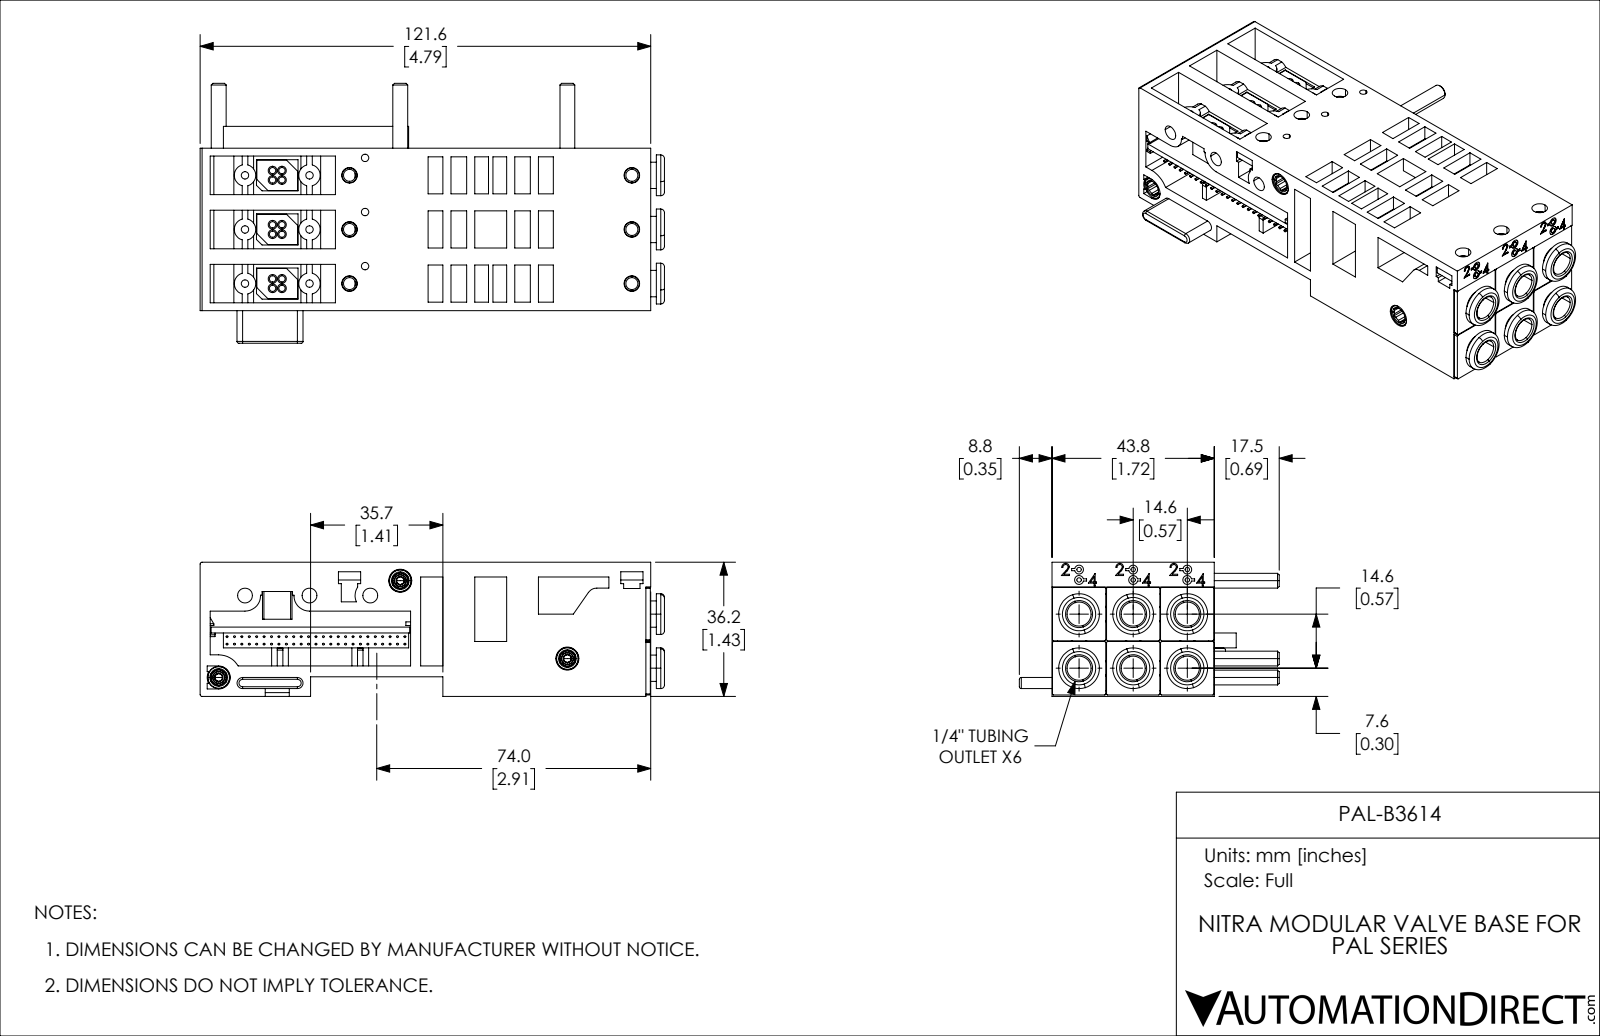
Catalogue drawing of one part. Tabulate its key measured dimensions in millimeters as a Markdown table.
| quantity | value |
| --- | --- |
| part name | PAL-B3614 |
| STEP written by | SolidWorks 2019 (CONFIG_CONTROL_DESIGN) |
| units | millimeters |
| bodies | 7 solids, 1501 faces (811 planar, 520 cylindrical, 170 other) |
| overall size | 125.3 × 70.1 × 36.2 |
| volume | 117 600 mm³ |
| surface area | 64 650 mm² |
| round holes (diameter × count) | 0.5 × 50, 2 × 9, 3.3 × 9, 2.4 × 6, 4.2 × 6, 6.5 × 6, 4 × 3, 6.2 × 2, 4.8 × 1 |
| round bosses / shafts (diameter × count) | 11 × 6, 7.1 × 6, 5.8 × 6, 1.2 × 6, 6 × 3, 4 × 3, 4.5 × 2 |
| partial cylindrical surfaces (radius × count) | 0.5 × 11, 2.5 × 6, 7.5 × 6, 10 × 6, 1 × 5, 4 × 5, 0.9 × 4, 0.7 × 3 |
| main face-to-face distances | 36.2, 1.6, 19.1, 8.2, 43.8, 17.1, 18.7, 14.6, 10.5, 8.6 |
| hole center spacings | 2, 4, 14.6, 6, 8, 12, 10, 14 |
